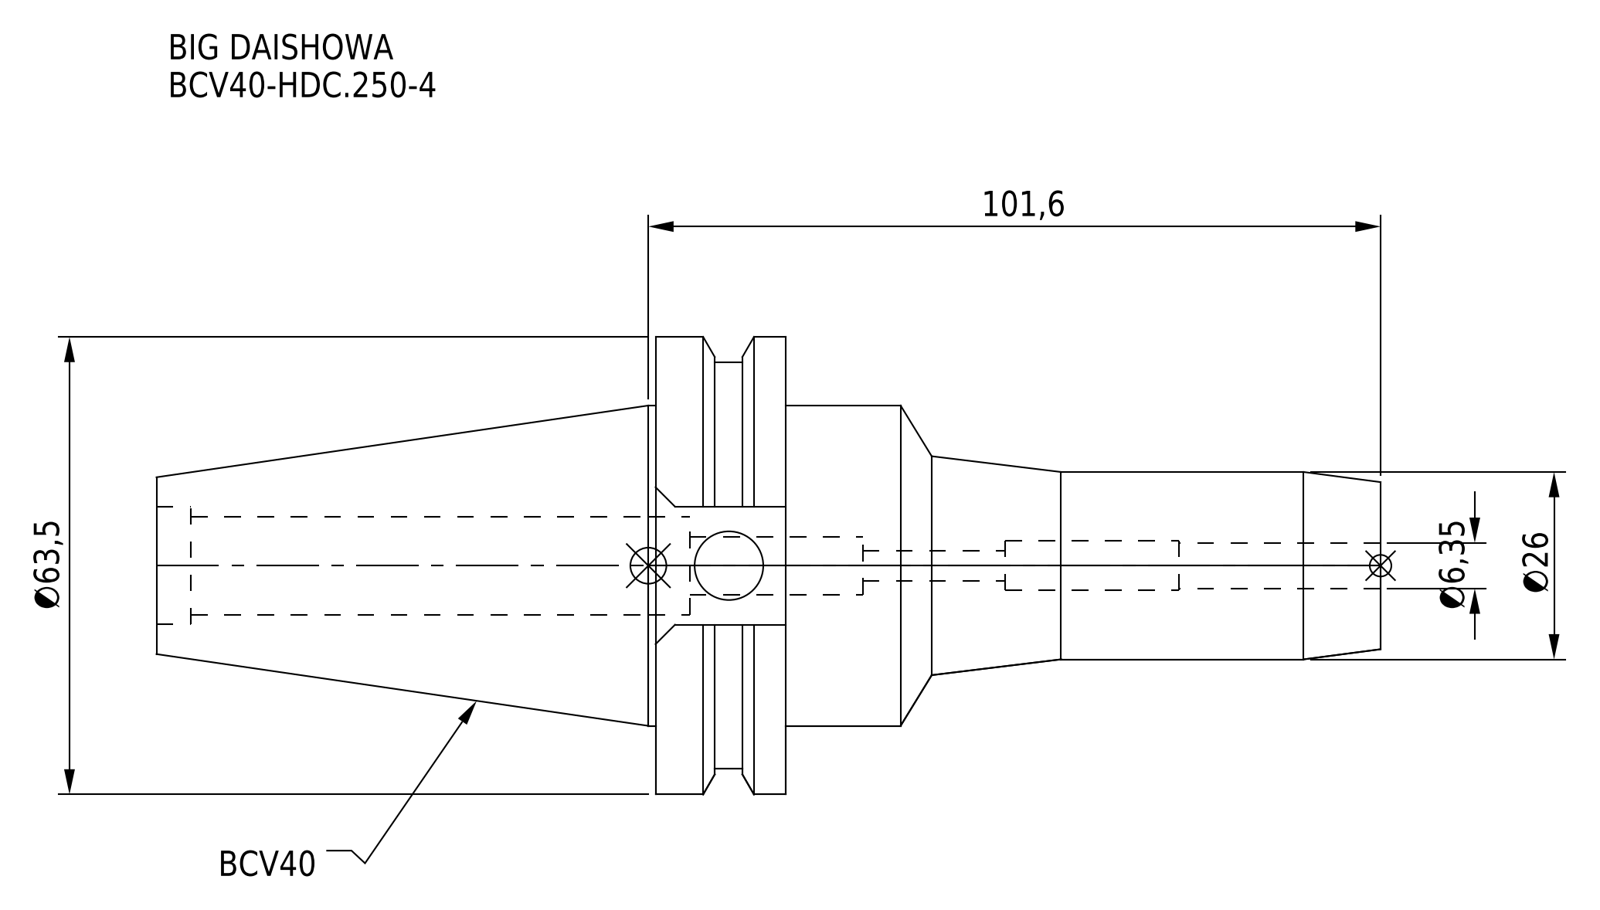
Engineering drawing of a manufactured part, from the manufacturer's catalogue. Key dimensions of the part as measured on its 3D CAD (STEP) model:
Part name (STEP PRODUCT): BCV40-HDC_250-4
STEP written by: CREO PARAMETRIC BY PTC INC, 2016380 (AUTOMOTIVE_DESIGN)
Units: millimetres
Bodies: 1 solid, 64 faces (24 planar, 28 cylindrical, 12 other)
Overall size (bounding box): 169.85 × 63.5 × 61.35
Volume: 166 205 mm³ · Surface area: 29 356 mm²
Round holes (diameter × count): ⌀4.2 ×1, ⌀6.35 ×1, ⌀6.9 ×1, ⌀8 ×1, ⌀9.53 ×1, ⌀13.6 ×1, ⌀16.32 ×1
Round bosses / shafts (diameter × count): ⌀63.5 ×1, ⌀56.36 ×1, ⌀44.45 ×1, ⌀26 ×1
Main face-to-face distances: 18.05, 82.55, 100.6, 169.85, 87.3, 69.25, 47.55, 16.38, 88.55, 6
